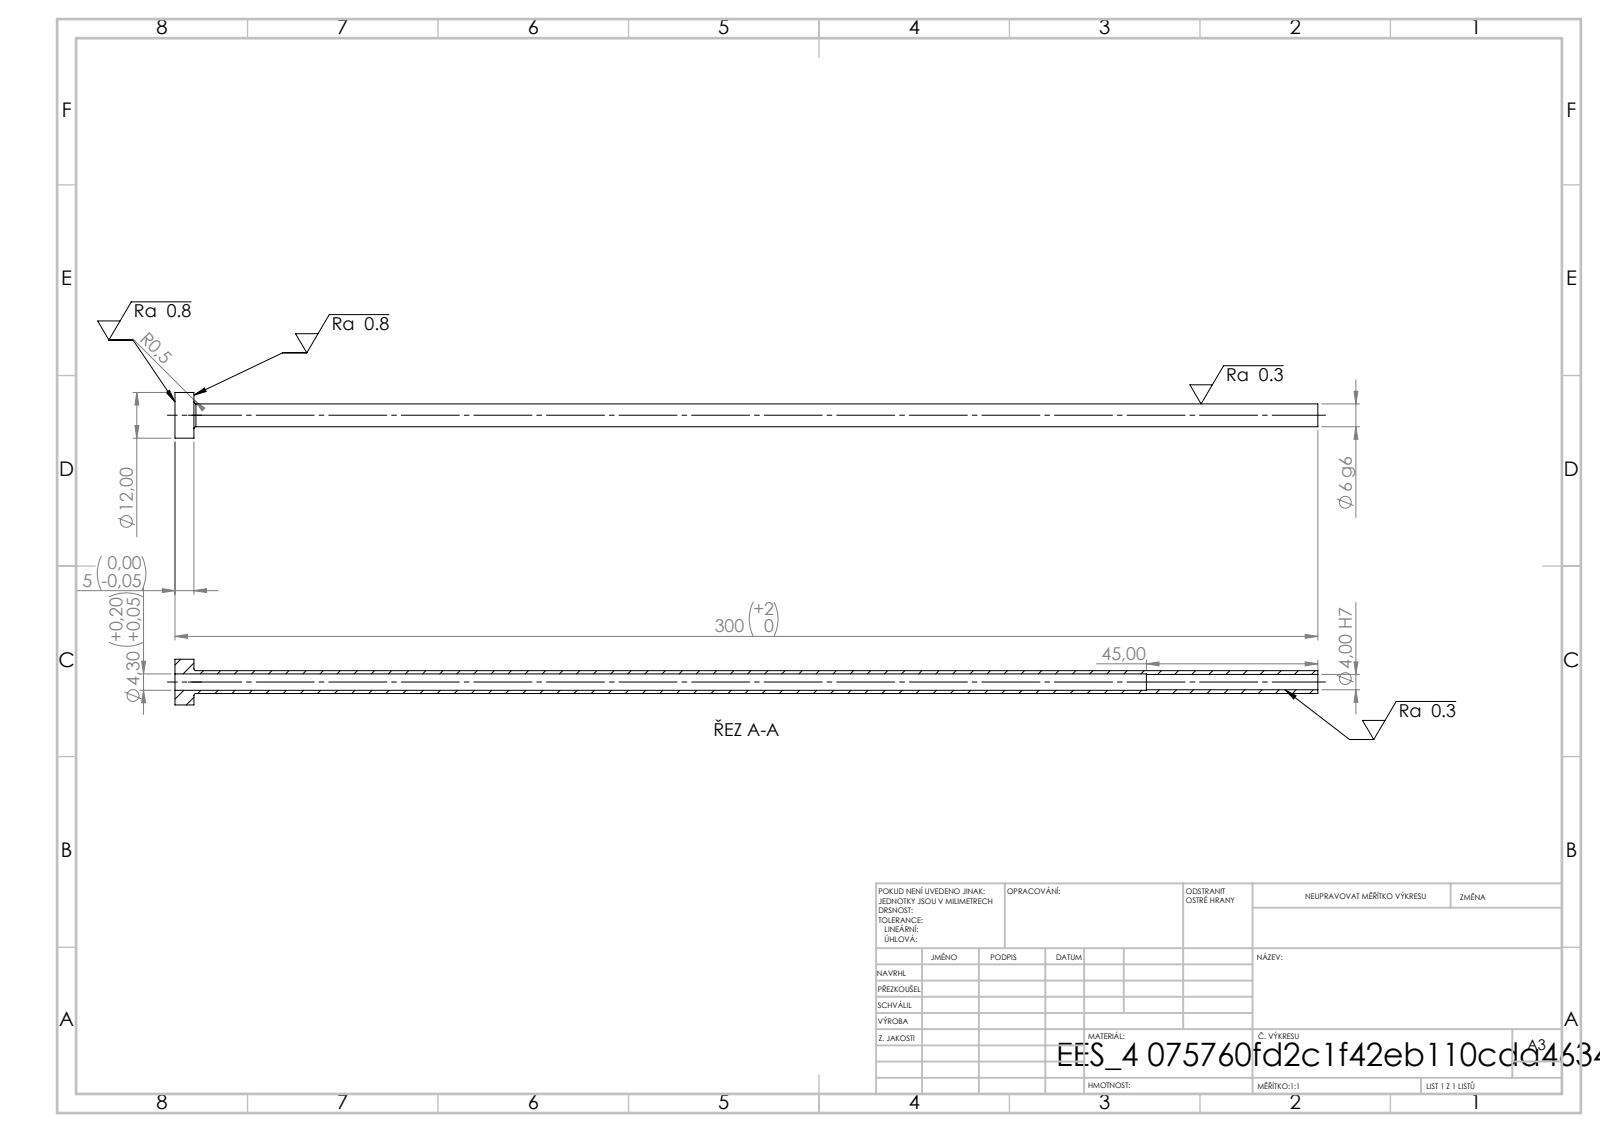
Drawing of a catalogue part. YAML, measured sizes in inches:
step_written_by: "SolidWorks 2019 (CONFIG_CONTROL_DESIGN)"
units: inches
bodies: {solids: 1, faces: 14, planar: 4, cylindrical: 8, other: 2}
overall_size: [11.811, 0.472, 0.472]
volume: 0.283
surface_area: 15.43
round_holes:
  - {diameter: 0.157, count: 1}
  - {diameter: 0.169, count: 1}
round_bosses_or_shafts:
  - {diameter: 0.472, count: 1}
  - {diameter: 0.236, count: 1}
face_to_face_distances: [0.197, 11.811, 11.614, 10.039, 9.843, 1.772]
